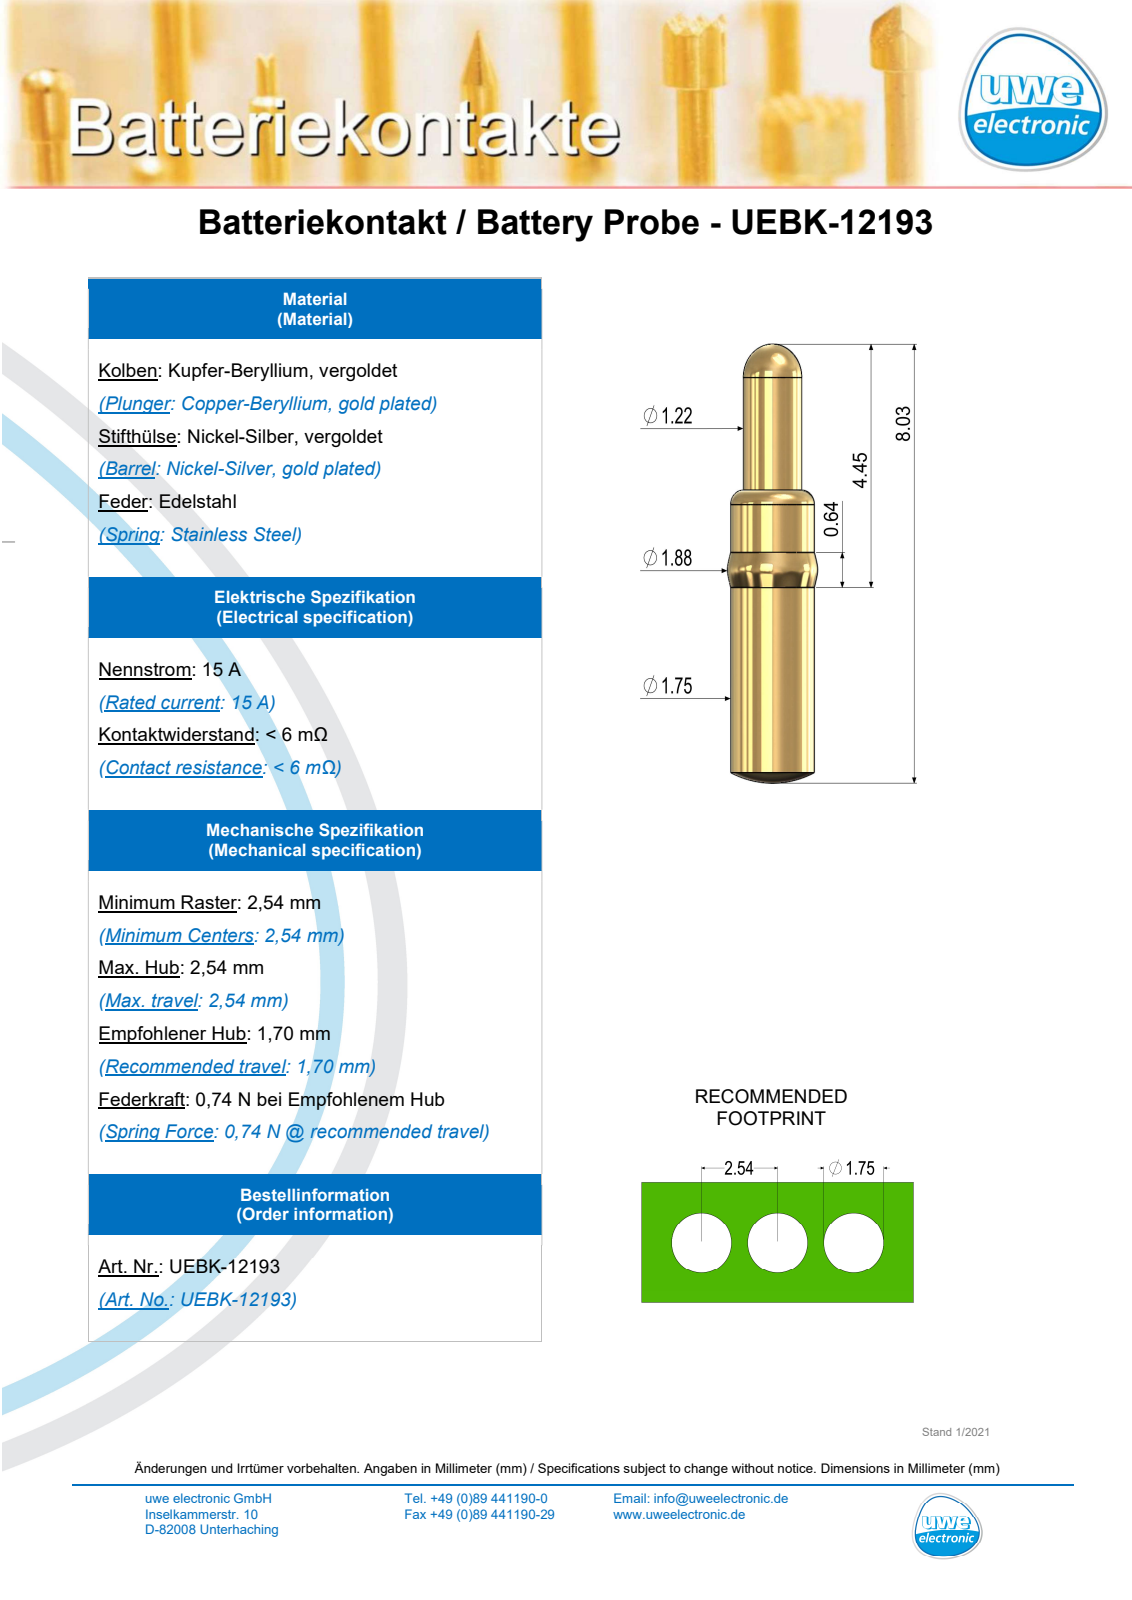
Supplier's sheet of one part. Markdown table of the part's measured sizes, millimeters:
| quantity | value |
| --- | --- |
| part name | UEBK-12193 |
| STEP written by | SolidWorks 2016 (AUTOMOTIVE_DESIGN) |
| units | millimeters |
| bodies | 1 solid, 14 faces (0 planar, 6 cylindrical, 8 other) |
| overall size | 8.03 × 1.89 × 1.89 |
| volume | 16 mm³ |
| surface area | 42 mm² |
| round bosses / shafts (diameter × count) | 1.75 × 1, 1.22 × 1 |
